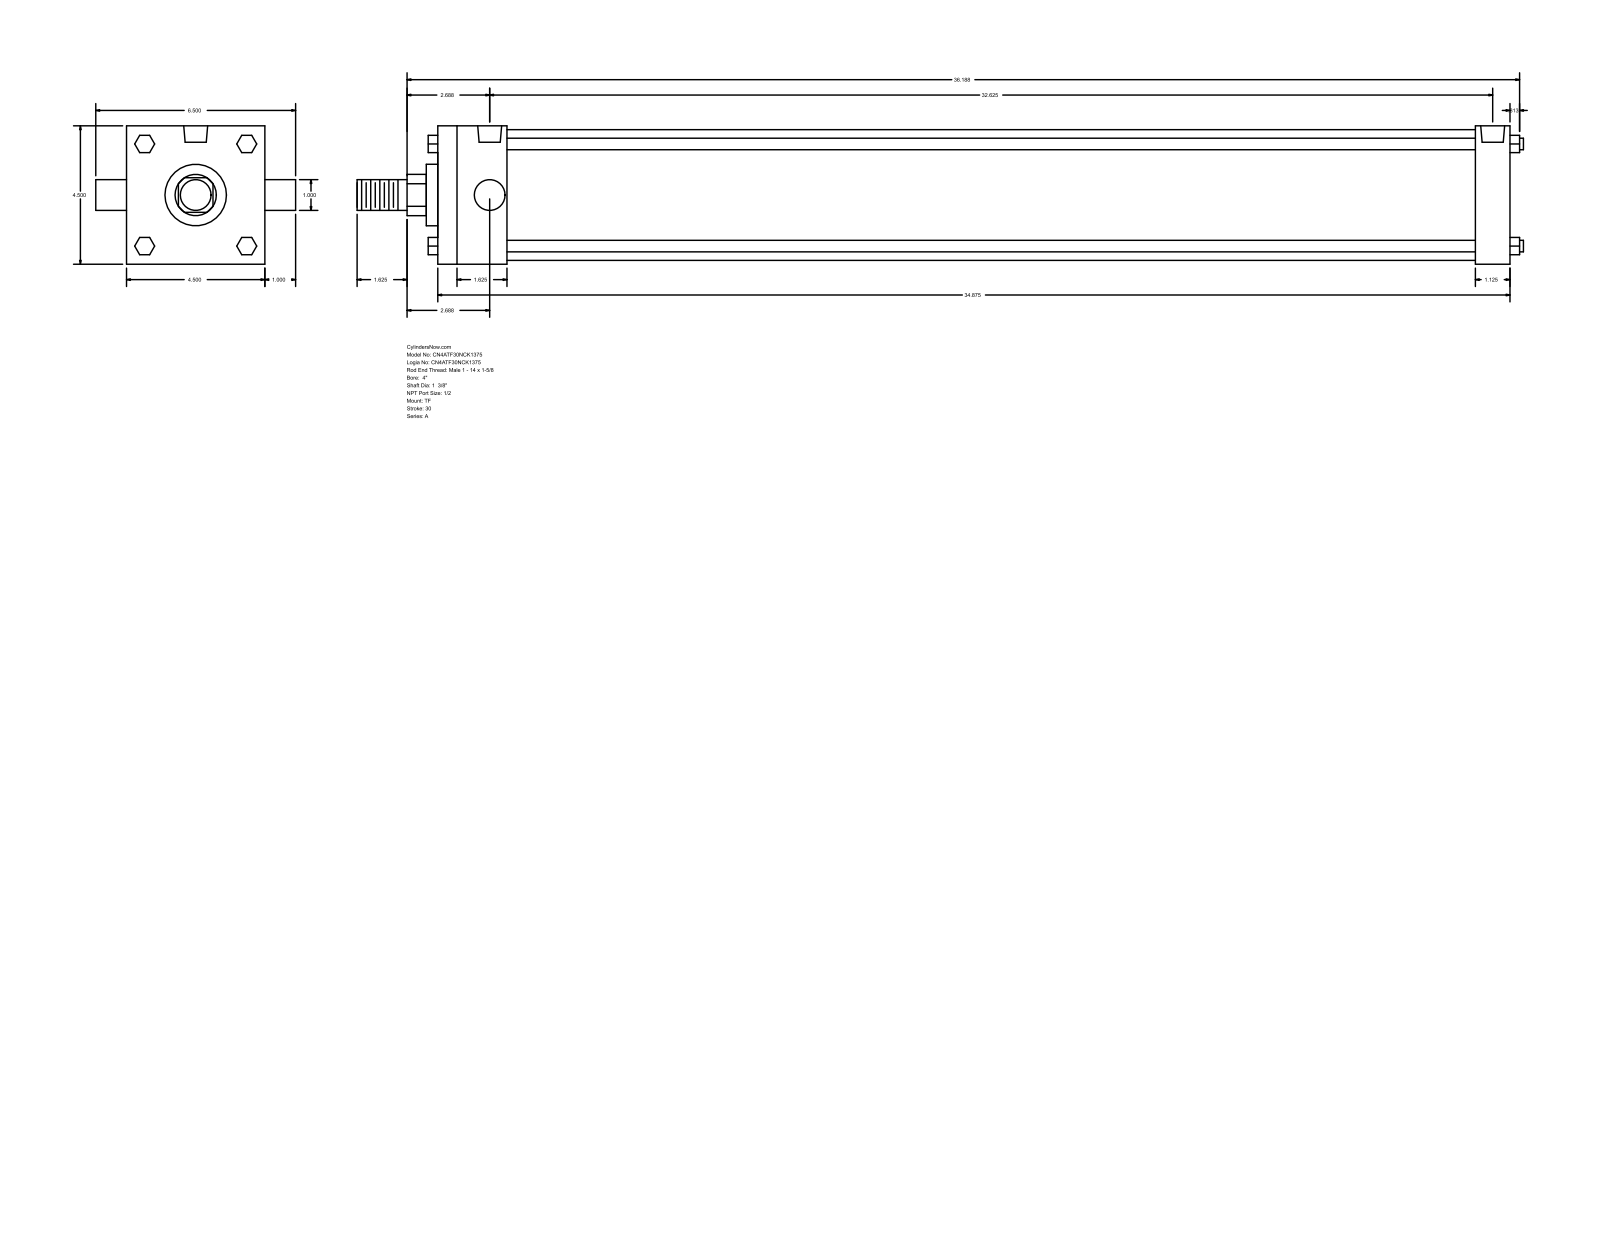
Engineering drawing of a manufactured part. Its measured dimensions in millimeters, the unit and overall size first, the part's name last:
Units: millimetres
Overall size (bounding box): 963.61 × 165.1 × 114.3
Round holes (diameter × count): ⌀8.73 ×3, ⌀19.77 ×2
Round bosses / shafts (diameter × count): ⌀9.53 ×4, ⌀25.4 ×2, ⌀107.95 ×1, ⌀50.8 ×1, ⌀34.92 ×1
Partial cylindrical surfaces — rounded edges, fillets, slot ends (radius × count): R17.06 ×1
Main face-to-face distances: 114.3, 885.83, 57.15, 28.58, 857.25, 800.1, 828.68, 66.67, 14.29, 25.4
Hole centre spacings: 3.18, 825.5, 822.32, 828.68
Bodies: 0 solids, 120 faces (92 planar, 28 cylindrical, 0 other)
Part name (STEP PRODUCT): A_TF__0400_1.375
STEP written by: GSSL Pune (CONFIG_CONTROL_DESIGN)
